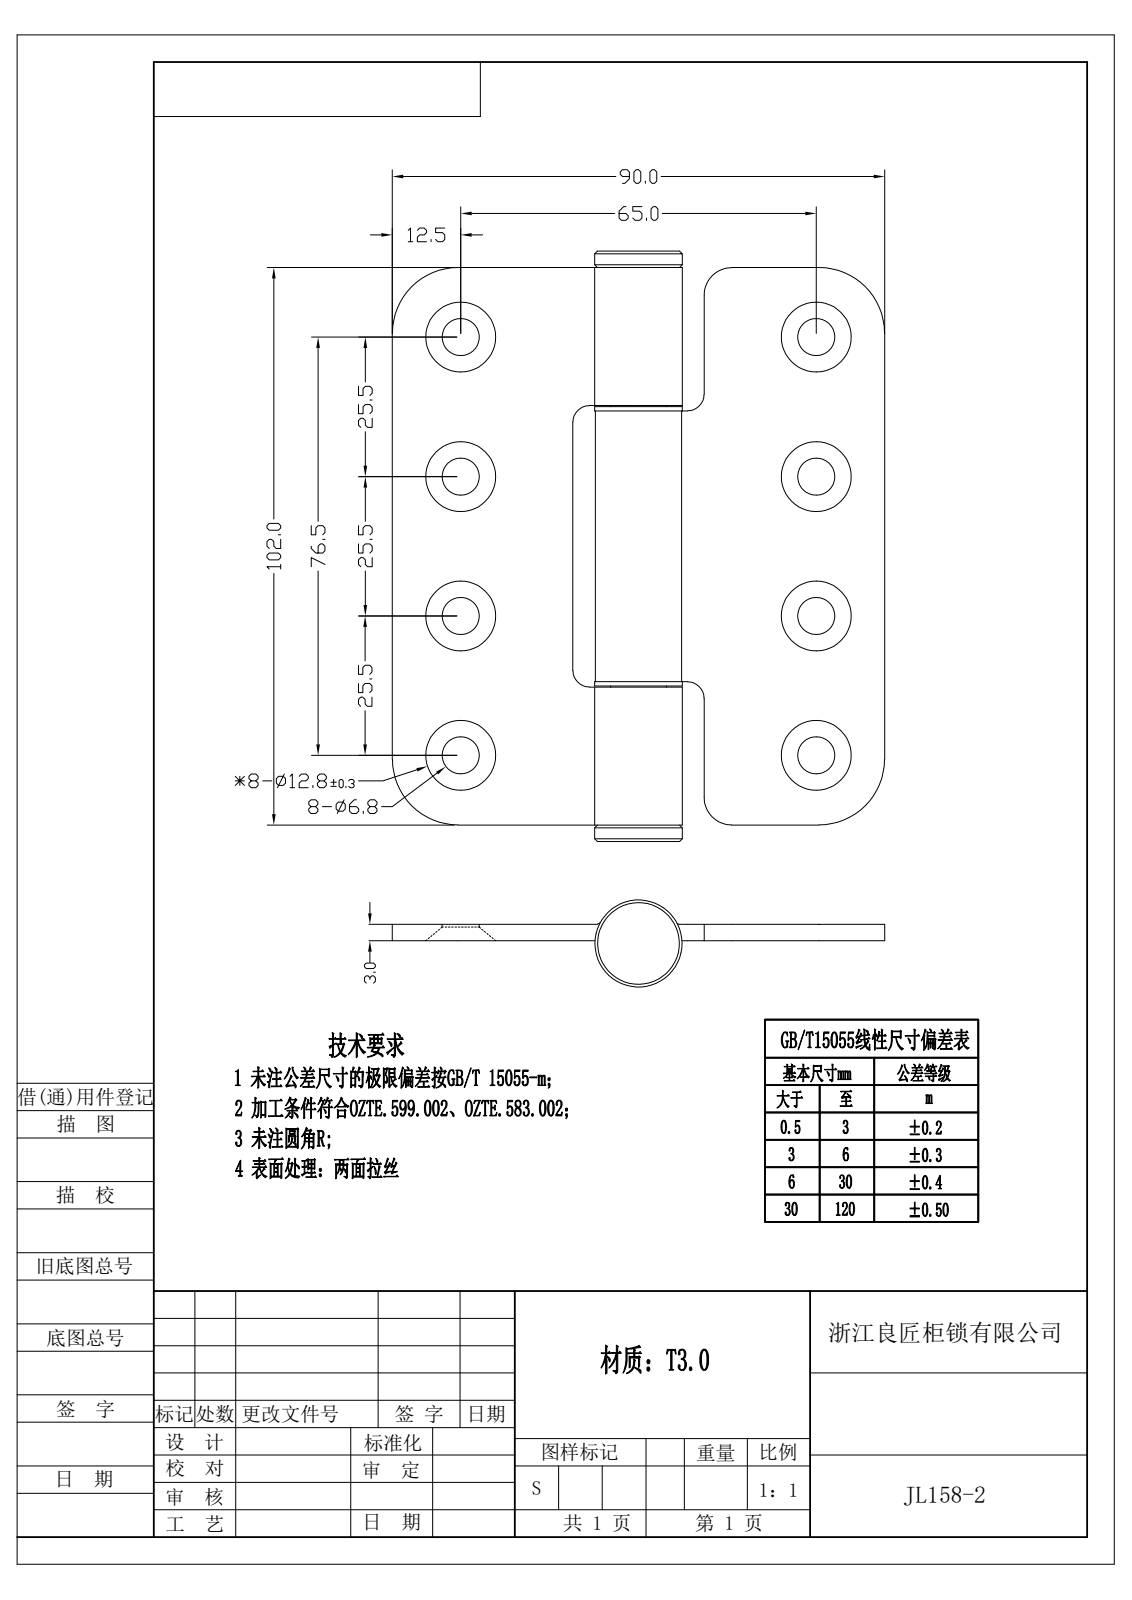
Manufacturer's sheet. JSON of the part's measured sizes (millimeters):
{"step_written_by": "Rhino 8.5 (CONFIG_CONTROL_DESIGN)", "units": "millimeters", "bodies": {"solids": 3, "faces": 92, "planar": 24, "cylindrical": 44, "other": 24}, "overall_size": [108, 90, 16], "volume_mm3": 40496, "surface_area_mm2": 28088, "round_holes": [[6.8, 8], [10, 1]], "round_bosses_or_shafts": [[16, 1]], "partial_cylinders_radius": [[1.5, 4], [6, 4], [12, 4], [5, 2]], "face_to_face_distances": [3, 105, 102, 33, 57, 29.25, 78.75, 26.25, 75.75, 28.25], "hole_center_spacings": [25.5, 69.82, 51, 65, 82.62, 76.5, 100.39]}
